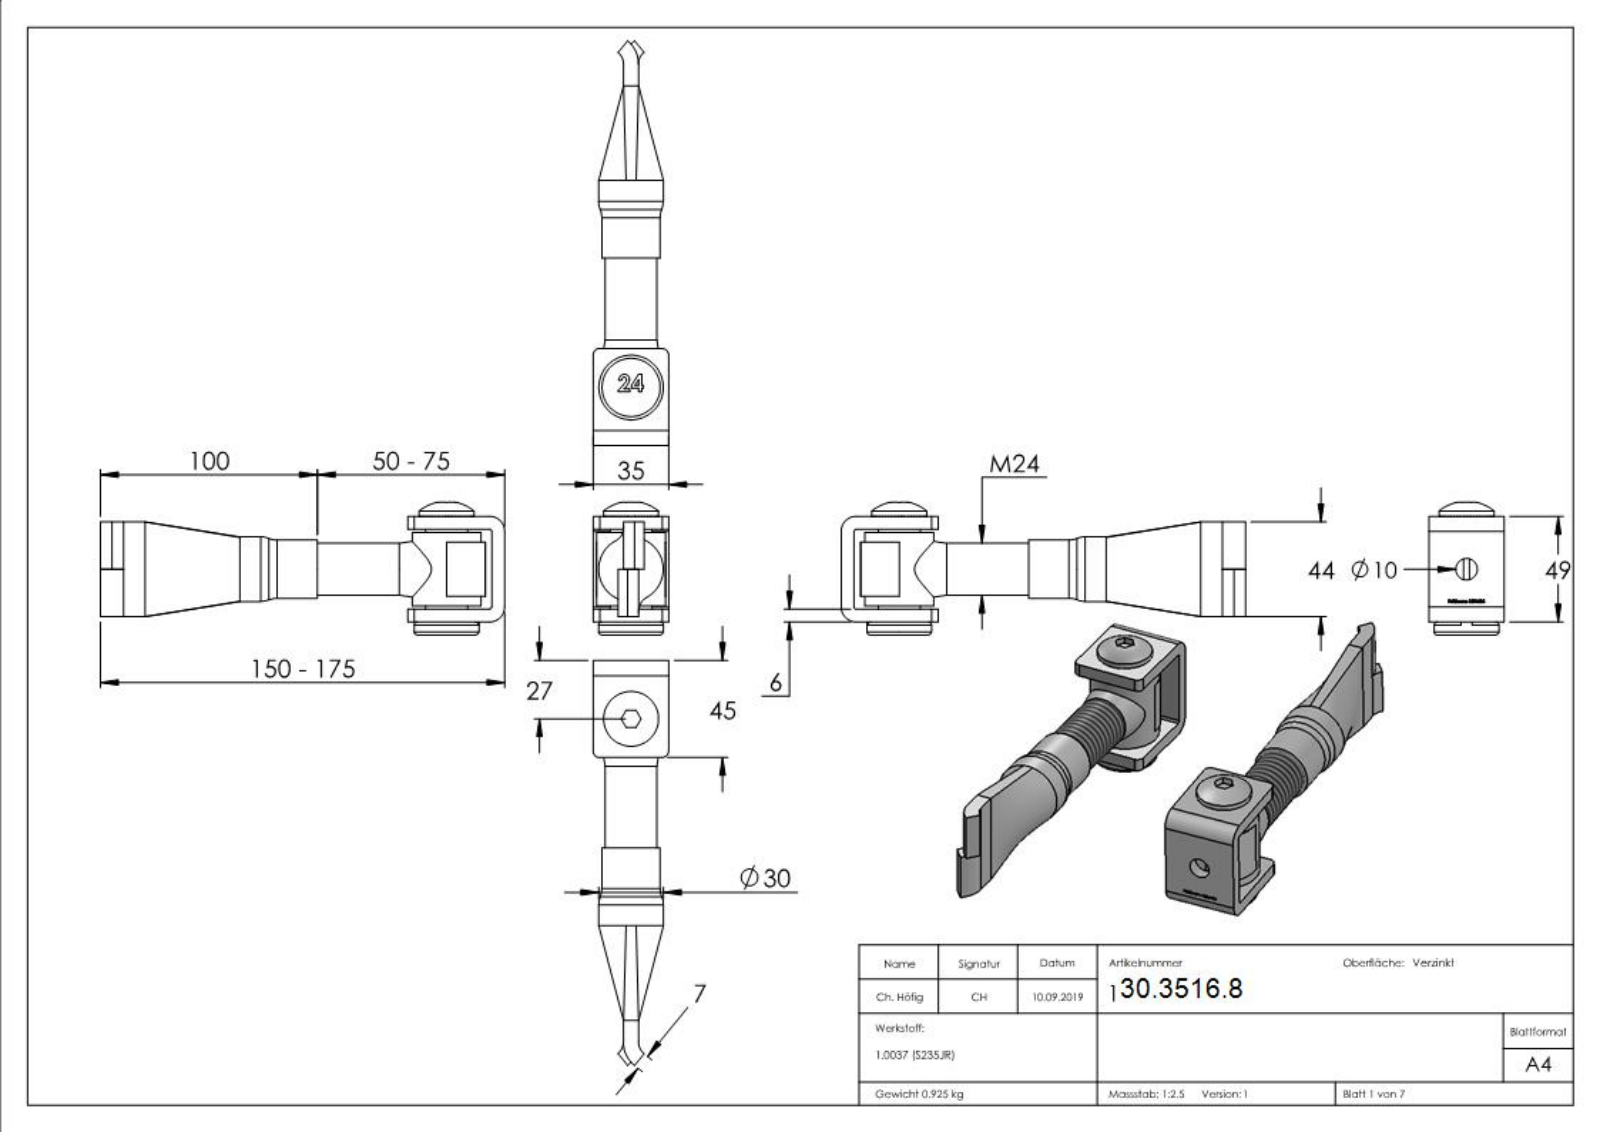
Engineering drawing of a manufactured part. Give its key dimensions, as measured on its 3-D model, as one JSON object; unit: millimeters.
{"part_name": "125-M24; 125-MXX Teil5_125-M24 Teil5; 125-MXX Teil4_125-M24 Teil4; 125-MXX Teil2_125-M24 Teil2 (+2 more)", "step_written_by": "SolidWorks 2015 (CONFIG_CONTROL_DESIGN)", "units": "millimeters", "bodies": {"solids": 5, "faces": 504, "planar": 345, "cylindrical": 49, "other": 110}, "overall_size": [187.77, 61.6, 35], "volume_mm3": 118579, "surface_area_mm2": 45671, "round_holes": [[20, 2], [10, 1], [10.2, 1], [12.6, 1], [19.9, 1], [21, 1]], "round_bosses_or_shafts": [[30, 2], [32, 1], [27, 1], [25.5, 1], [24, 1], [19.5, 1], [12, 1]], "partial_cylinders_radius": [[1, 2], [3, 2], [6.93, 2], [7, 2], [13.93, 2], [17, 2], [3.1, 1], [10, 1]], "face_to_face_distances": [6, 43, 49, 41.5, 37, 1.5, 7.5, 35.5, 14, 21]}
